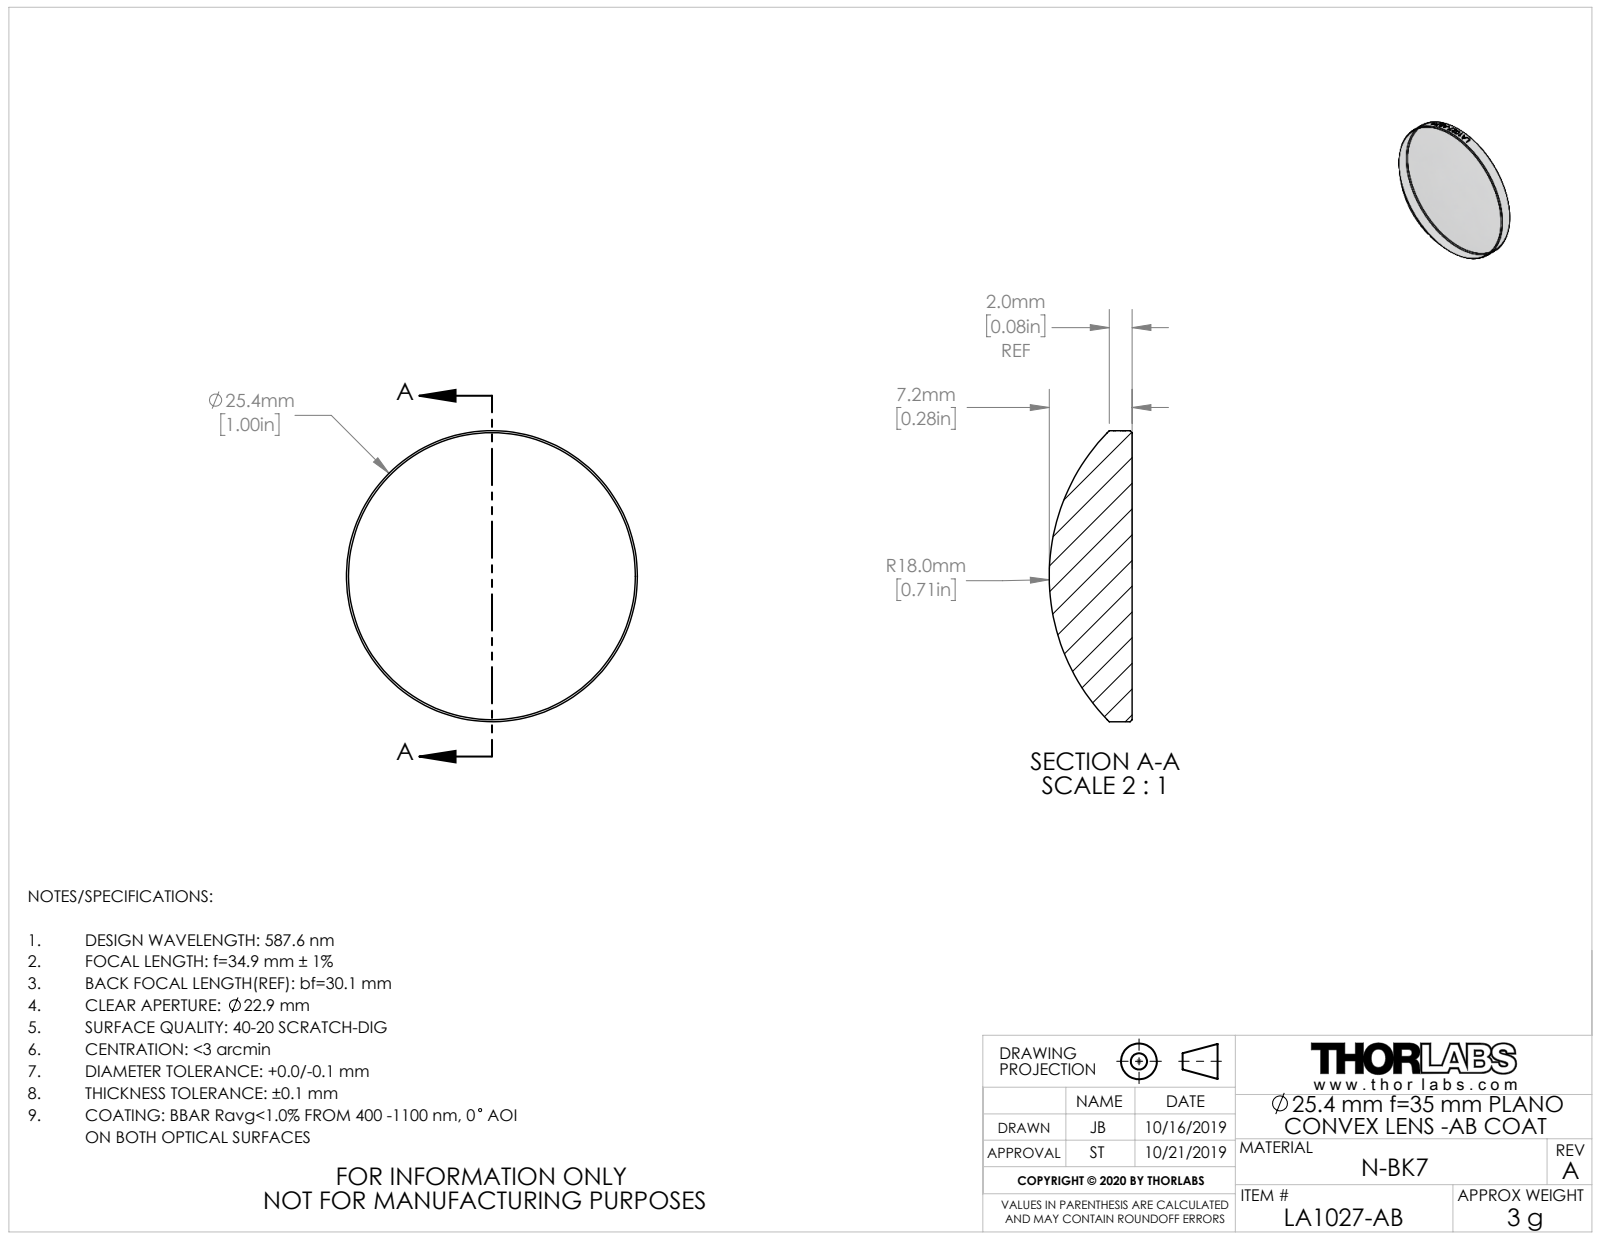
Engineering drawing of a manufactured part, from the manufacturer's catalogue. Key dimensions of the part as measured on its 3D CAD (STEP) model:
Part name (STEP PRODUCT): TTN195782-E0W
STEP written by: SolidWorks 2018 (CONFIG_CONTROL_DESIGN)
Units: inches
Bodies: 1 solid, 27 faces (1 planar, 20 cylindrical, 6 other)
Overall size (bounding box): 1 × 1 × 0.285
Volume: 0.147 in³ · Surface area: 1.938 in²
Round bosses / shafts (diameter × count): ⌀1 ×1
